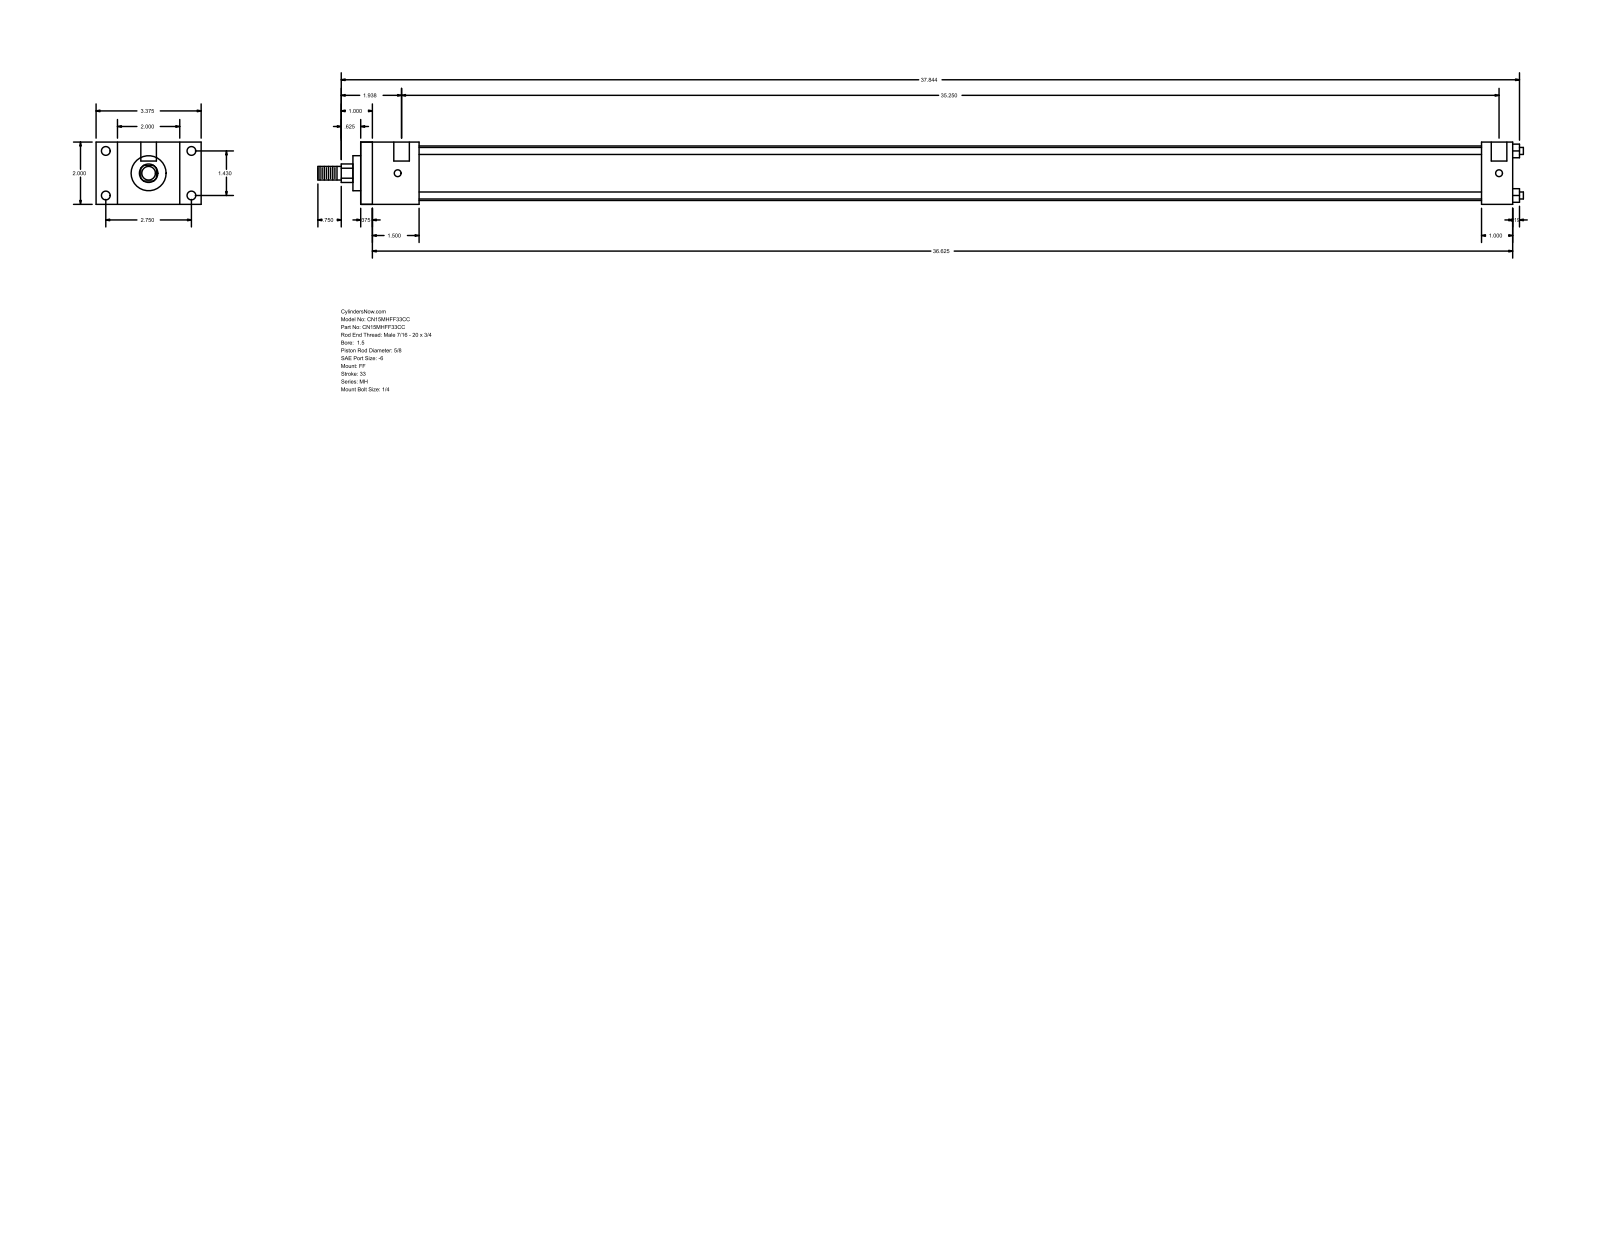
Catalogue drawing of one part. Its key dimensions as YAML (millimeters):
part_name: "MH_FF__0150_0.625"
step_written_by: "GSSL Pune (CONFIG_CONTROL_DESIGN)"
units: millimeters
bodies: {solids: 0, faces: 92, planar: 64, cylindrical: 28, other: 0}
overall_size: [983.46, 85.72, 50.8]
round_holes:
  - {diameter: 5.56, count: 4}
  - {diameter: 7.14, count: 4}
  - {diameter: 12.7, count: 2}
round_bosses_or_shafts:
  - {diameter: 5.71, count: 4}
  - {diameter: 44.45, count: 1}
  - {diameter: 28.57, count: 1}
  - {diameter: 15.88, count: 1}
  - {diameter: 11.11, count: 1}
partial_cylinders:
  - {radius: 7.54, count: 1}
face_to_face_distances: [50.8, 939.79, 930.27, 9.52, 25.4, 17.46, 68.26, 47.62, 38.1, 892.17]
hole_center_spacings: [36.32, 69.84, 78.72, 898.52, 3.17, 895.35]
